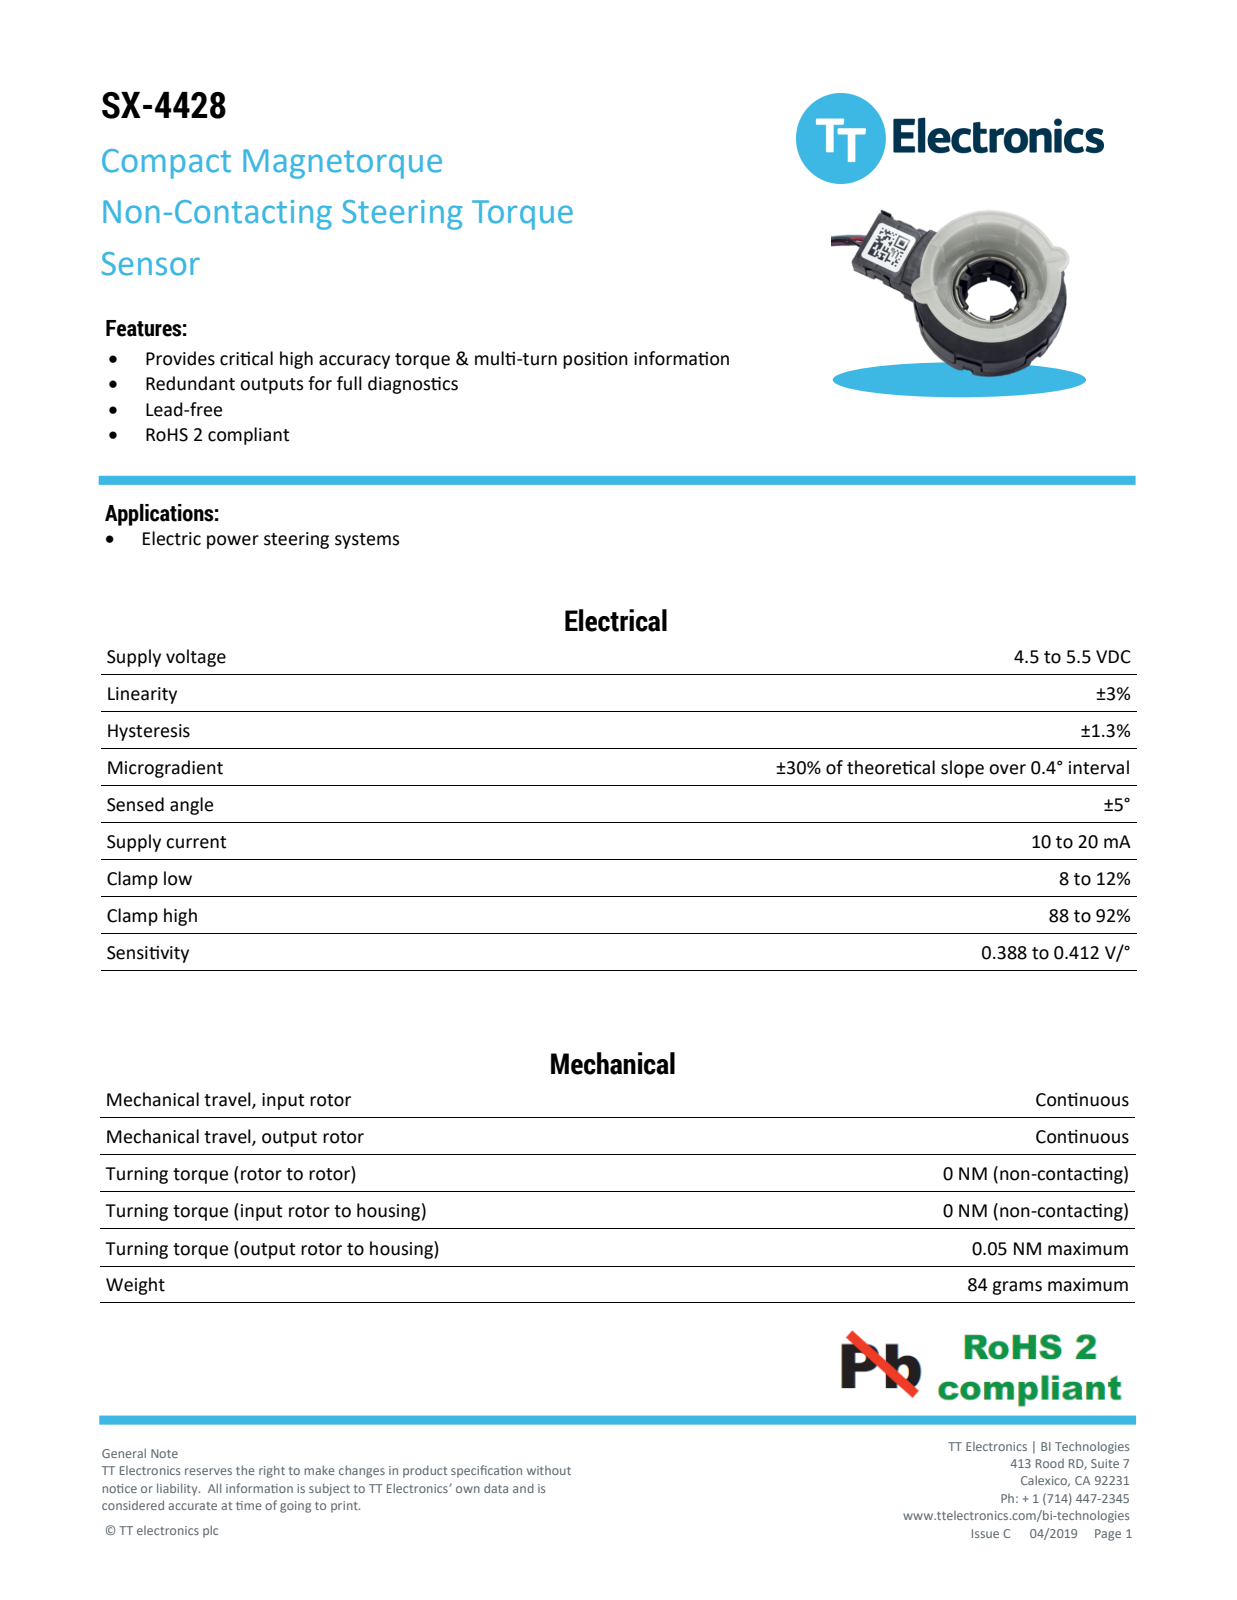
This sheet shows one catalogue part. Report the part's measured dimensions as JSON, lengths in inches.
{"part_name": "SX-4428A_SW0012", "step_written_by": "PRO/ENGINEER BY PARAMETRIC TECHNOLOGY CORPORATION, 2012060 (CONFIG_CONTROL_DESIGN)", "units": "inches", "bodies": {"solids": 7, "faces": 3416, "planar": 2492, "cylindrical": 431, "other": 493}, "overall_size": [9.334, 2.354, 1.475], "volume_in3": 3.591, "surface_area_in2": 54.3, "round_holes": [[0.242, 1], [1.142, 1], [1.152, 1], [1.654, 1], [1.969, 1]], "round_bosses_or_shafts": [[0.063, 20], [2.28, 1], [2.047, 1], [1.732, 1], [0.25, 1]], "partial_cylinders_radius": [[0.008, 28], [0.039, 23], [0.033, 16], [0.01, 14], [0.012, 6], [0.014, 5], [0.062, 4], [0.157, 4]], "face_to_face_distances": [0.734, 0.039, 0.034, 0.069, 0.665, 1.272, 0.607, 0.538, 0.472, 0.05]}
